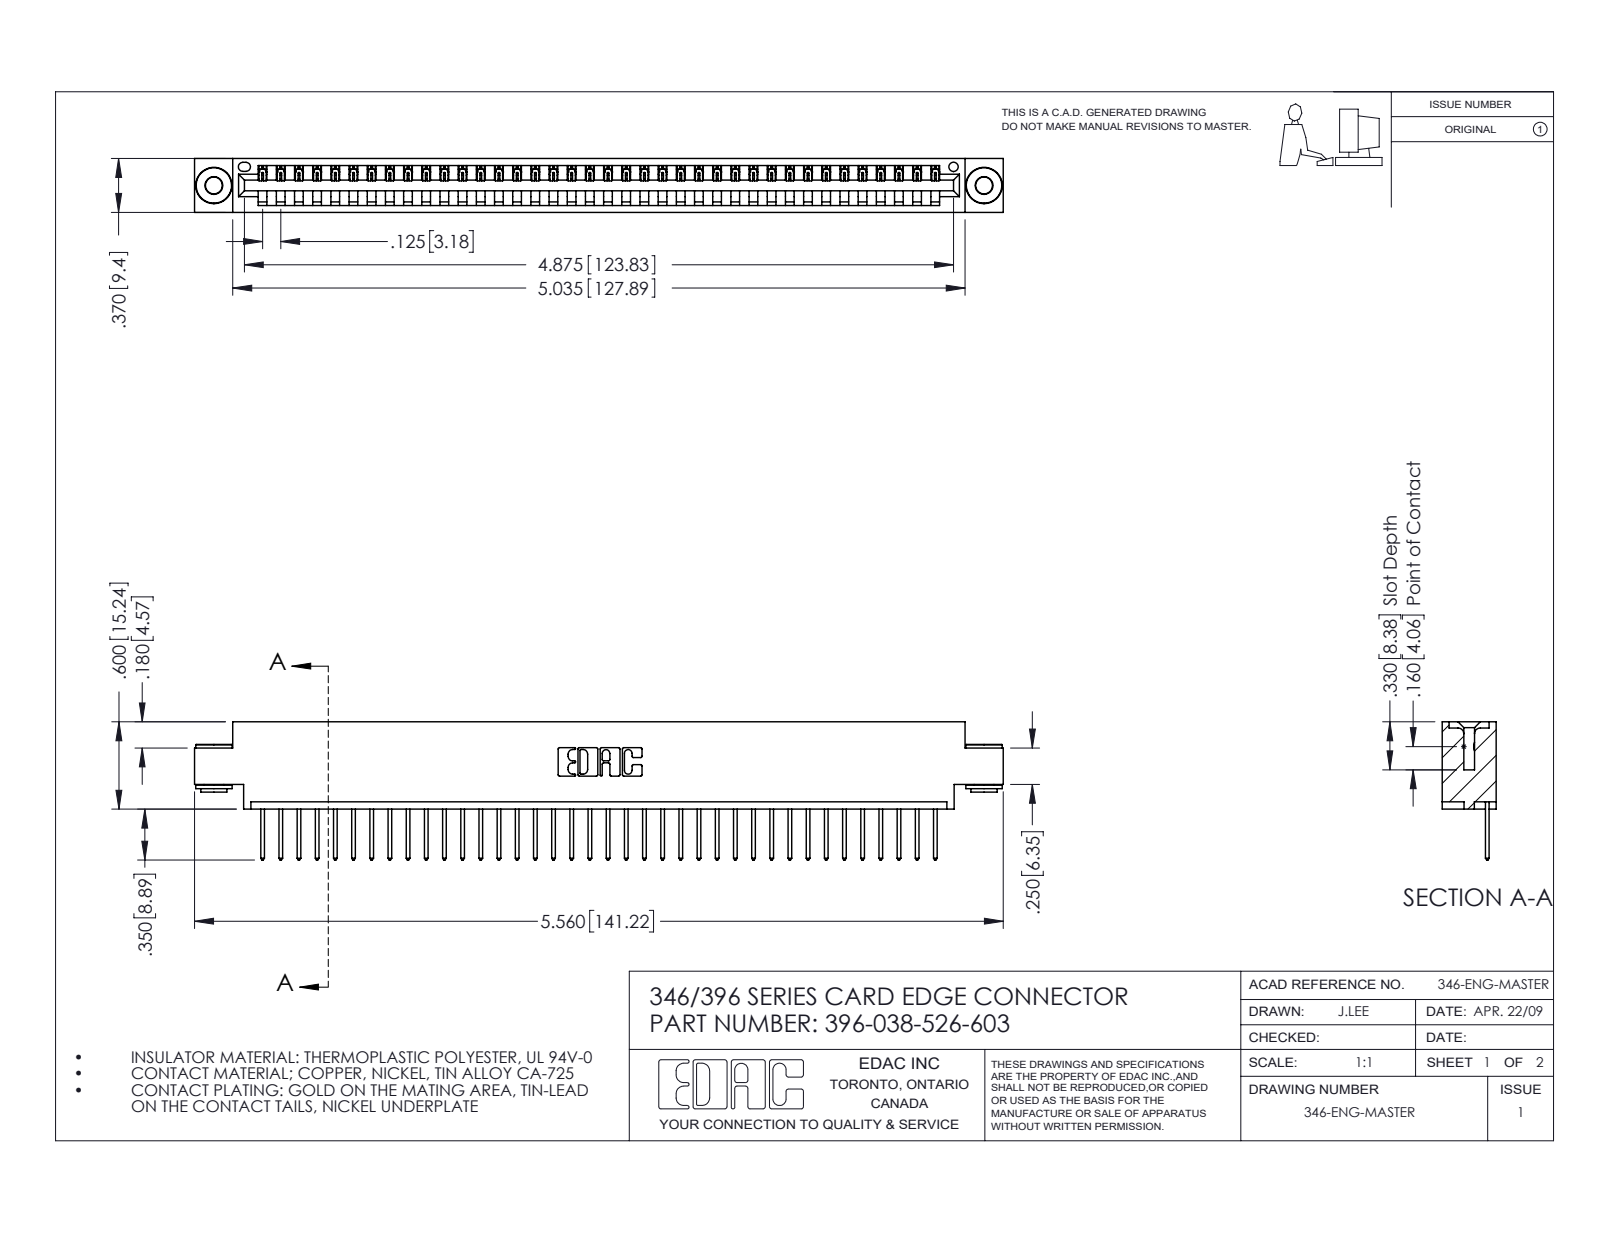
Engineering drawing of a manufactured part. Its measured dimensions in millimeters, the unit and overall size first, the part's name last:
Units: millimetres
Overall size (bounding box): 141.2 × 24.1 × 9.4
Round holes (diameter × count): ⌀2.9 ×2, ⌀4 ×2, ⌀1.6 ×1
Round bosses / shafts (diameter × count): ⌀6.4 ×2, ⌀4.6 ×2, ⌀3.5 ×2
Partial cylindrical surfaces — rounded edges, fillets, slot ends (radius × count): R0.2 ×76, R0.3 ×76, R0.3 ×22, R0.2 ×6, R0.8 ×6, R0.7 ×3, R0.8 ×2, R1 ×2
Main face-to-face distances: 1.2, 8.2, 9.4, 6.4, 0.6, 1.8, 7.6, 3.8, 5.6, 2.5
Hole centre spacings: 6.2, 129.2, 134.5
Volume: 13 300 mm³ · Surface area: 16 950 mm²
Bodies: 41 solids, 2368 faces (1610 planar, 750 cylindrical, 8 other)
Part name (STEP PRODUCT): 345-250-002_345-250-002-102; 345-292-001_345-293-126; 396-038-526-603; 346 Part_0.170 Offset - 0.156 Dia-TH
STEP written by: SolidWorks 2016 (CONFIG_CONTROL_DESIGN)
